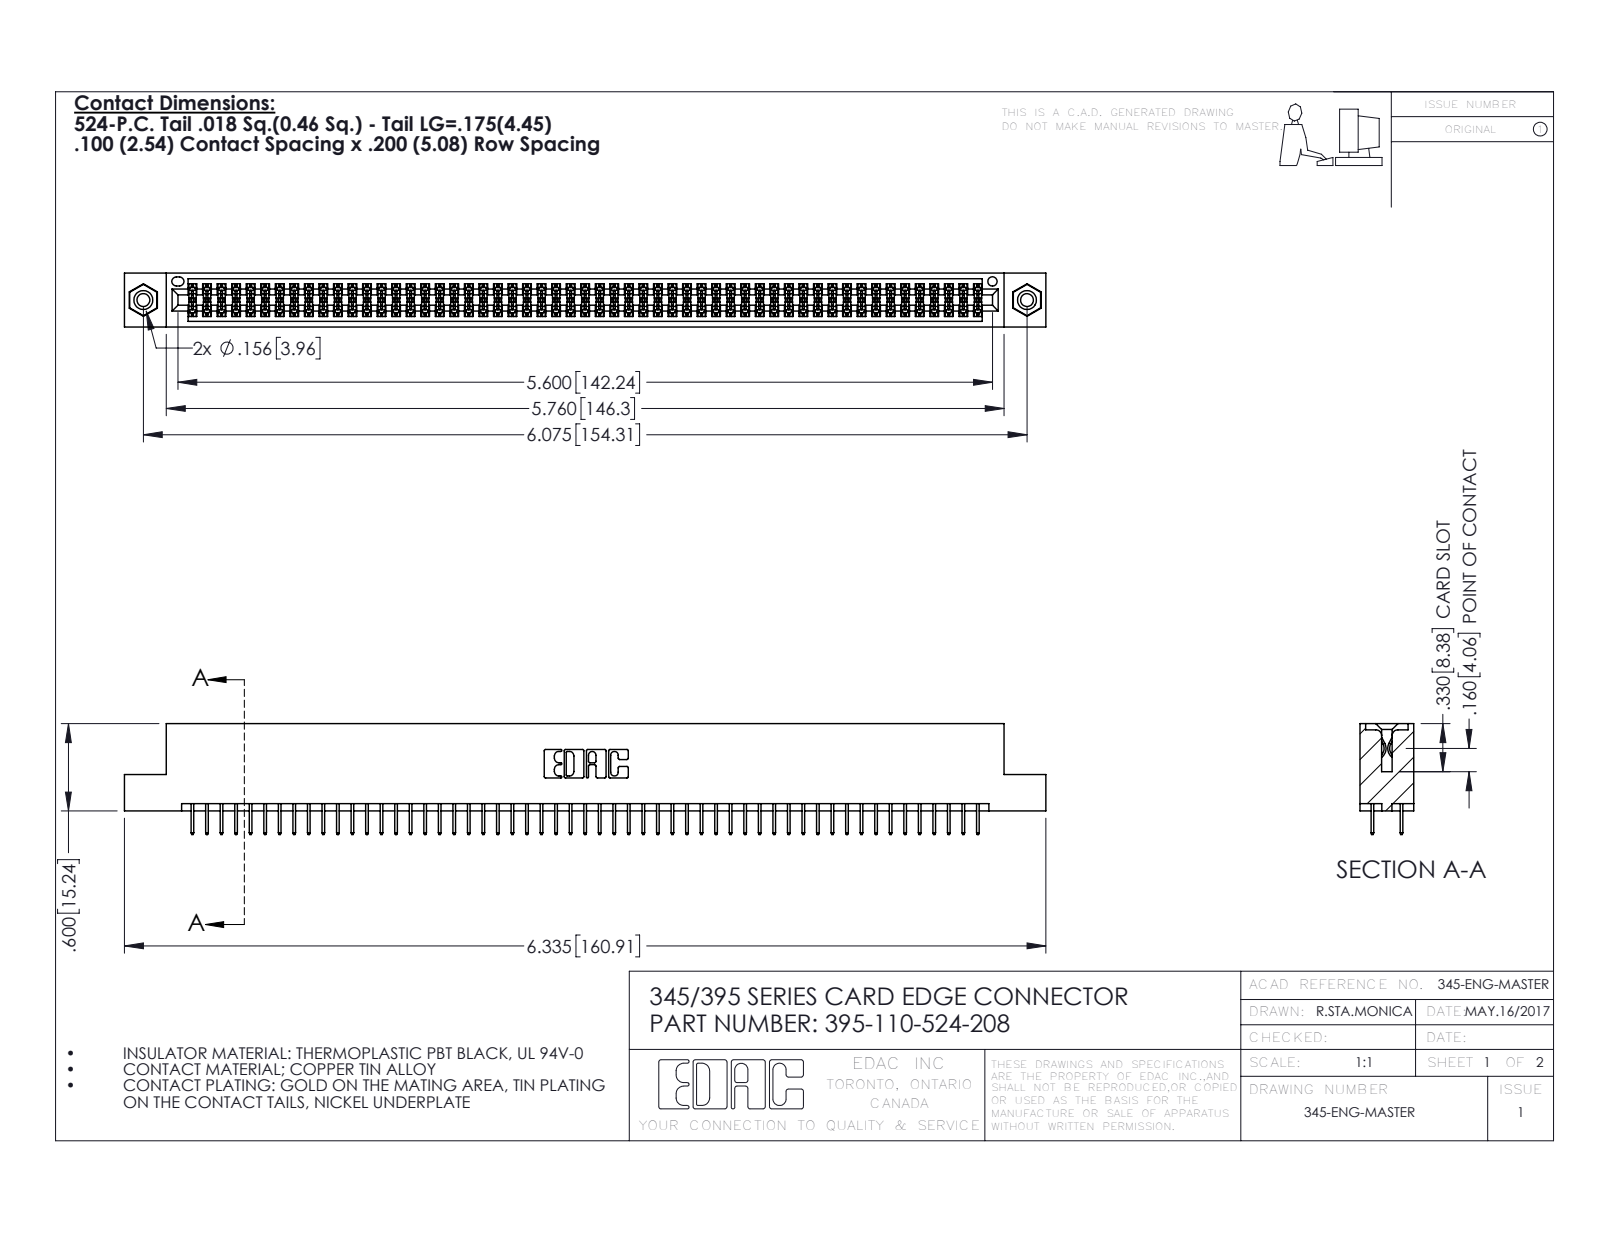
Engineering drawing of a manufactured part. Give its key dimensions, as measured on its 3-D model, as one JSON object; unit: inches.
{"part_name": "345-292-001_345-293-124; 345-250-001_345-250-003-102; 345 Part_Flush Mounting Lugs - 0.156 Dia-TI; 395-110-524-208", "step_written_by": "SolidWorks 2016 (CONFIG_CONTROL_DESIGN)", "units": "inches", "bodies": {"solids": 113, "faces": 6126, "planar": 4402, "cylindrical": 1708, "other": 16}, "overall_size": [6.335, 0.762, 0.37], "volume_in3": 0.951, "surface_area_in2": 35.42, "round_holes": [[0.089, 2], [0.125, 2], [0.156, 2], [0.064, 1]], "round_bosses_or_shafts": [[0.155, 2]], "partial_cylinders_radius": [[0.006, 165], [0.01, 22], [0.007, 6], [0.031, 6], [0.026, 3], [0.014, 2], [0.019, 2], [0.022, 2]], "face_to_face_distances": [0.072, 0.298, 0.2, 0.37, 0.098, 0.272, 0.025, 0.225, 0.072, 0.175], "hole_center_spacings": [0.27, 5.839, 6.075]}
